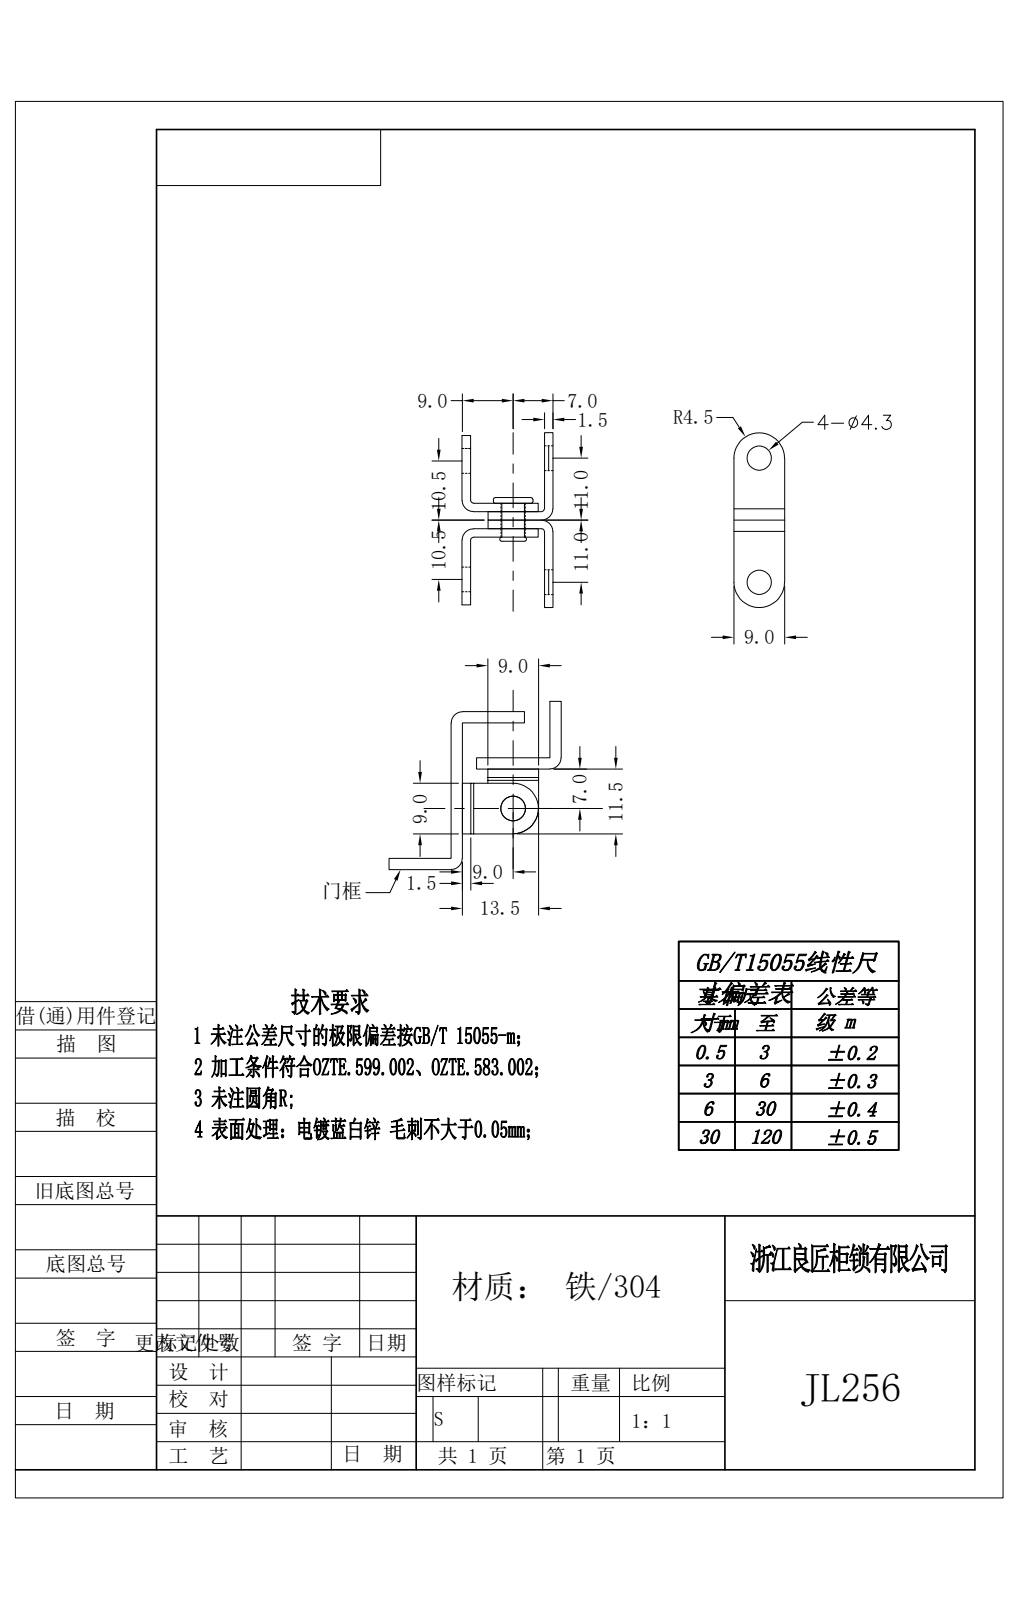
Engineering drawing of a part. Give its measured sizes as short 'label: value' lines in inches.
written by: Rhino 8.5 (CONFIG_CONTROL_DESIGN)
unit: in
bodies: 5 solids, 71 faces (27 planar, 36 cylindrical, 8 other)
size: 1.181 × 0.709 × 0.354
volume: 0.074 in³; area: 3.309 in²
holes: 5× ⌀0.169
bosses: 1× ⌀0.354, 1× ⌀0.276
rounds: 4× R0.02, 4× R0.079, 4× R0.177
face distances: 0.059, 0.118, 0.65, 0.177, 0.709, 0.591, 0.354, 0.236, 0.039, 0.098
hole spacings: 0.059, 0.768, 0.709, 0.827
